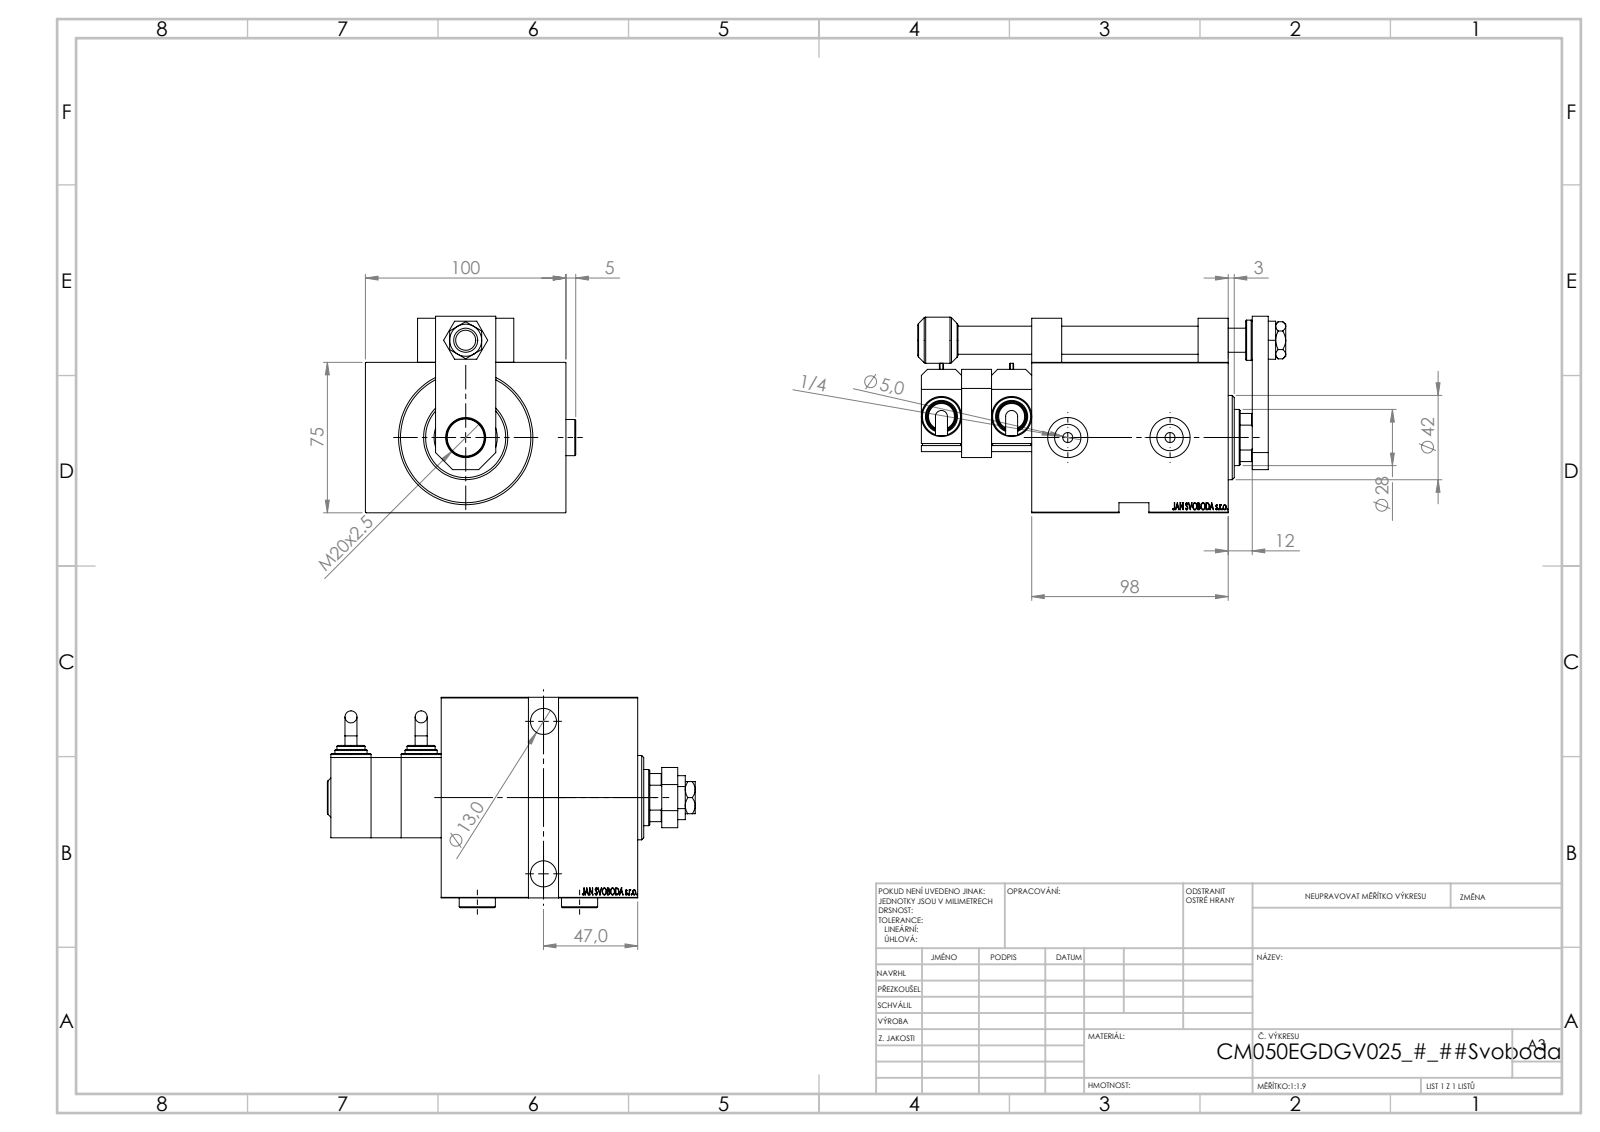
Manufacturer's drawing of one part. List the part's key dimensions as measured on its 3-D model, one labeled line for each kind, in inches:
Part name (STEP PRODUCT): NUT_D19_P; KROUZEK_PRO_TYC; V450CM_E_Body; V450CM_E_VCP (+7 more)
STEP written by: SolidWorks 2019 (CONFIG_CONTROL_DESIGN)
Units: inches
Bodies: 16 solids, 1127 faces (556 planar, 118 cylindrical, 453 other)
Overall size (bounding box): 7.224 × 4.13 × 3.858
Volume: 50.35 in³ · Surface area: 229.5 in²
Round holes (diameter × count): ⌀0.157 ×4, ⌀0.315 ×4, ⌀0.512 ×3, ⌀0.787 ×3, ⌀0.197 ×2, ⌀0.518 ×2, ⌀0.748 ×2, ⌀0.472 ×1, ⌀0.551 ×1, ⌀0.728 ×1, ⌀1.102 ×1, ⌀1.24 ×1
Round bosses / shafts (diameter × count): ⌀0.787 ×3, ⌀0.709 ×2, ⌀0.63 ×2, ⌀0.551 ×2, ⌀0.236 ×2, ⌀2.047 ×1, ⌀1.654 ×1, ⌀0.906 ×1
Partial cylindrical surfaces — rounded edges, fillets, slot ends (radius × count): R0.118 ×1, R0.531 ×1
Main face-to-face distances: 1.378, 2.953, 0.197, 3.858, 0.787, 3.937, 4.646, 0.591, 2.756, 1.181
Hole centre spacings: 0.787, 1.906, 2.037, 2.447, 2.55, 3.268, 3.361, 1.909
